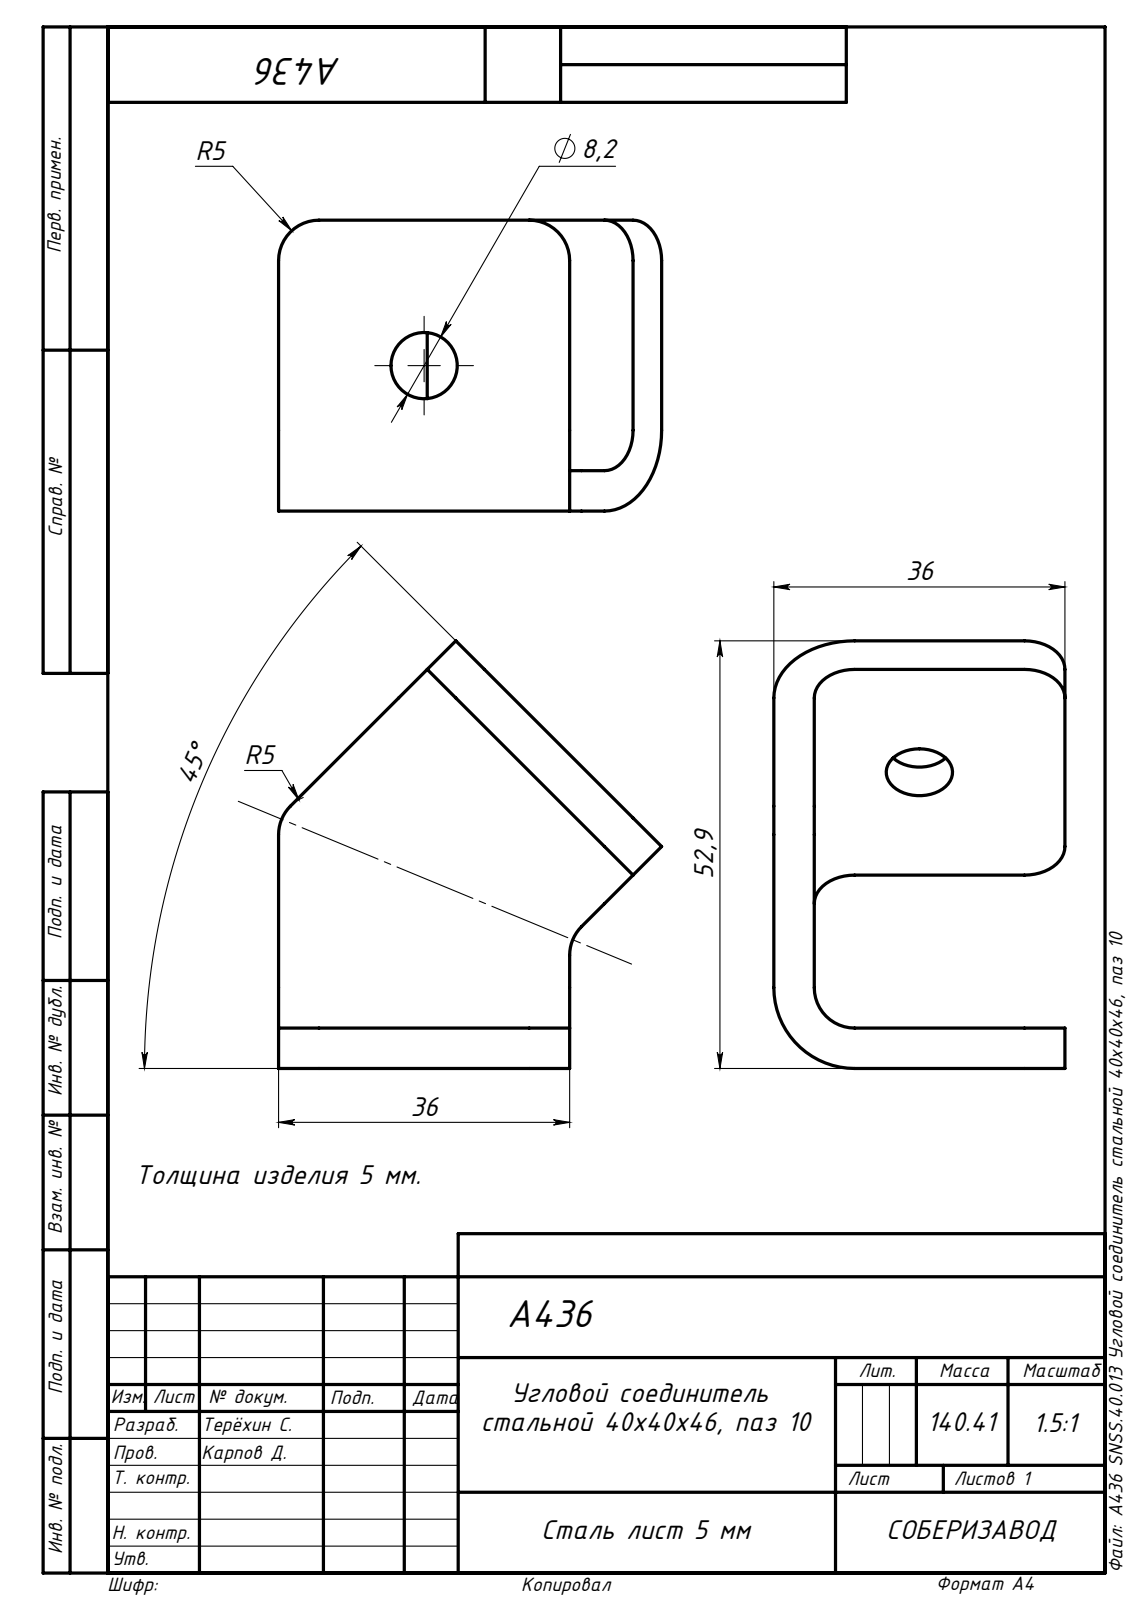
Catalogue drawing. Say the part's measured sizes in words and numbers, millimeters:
The part is named "A436 SNSS.40.013 Угловой соединитель стальной 40х40х46, паз 10". Its 3-D file was written by "SolidWorks 2020 (AUTOMOTIVE_DESIGN)". It is 1 solid with 34 faces: 20 planar, 14 cylindrical and 0 other. Overall it measures 52.92 by 47.38 by 36 millimeters. Its volume is 17 842 cubic millimeters and its surface area 8 736 square millimeters. Round holes: 2 of diameter 8.2. Partial cylindrical surfaces (rounded edges, fillets, slot ends): 8 of radius 5, 2 of radius 10. The main face-to-face distances are 5, 36, 31.
